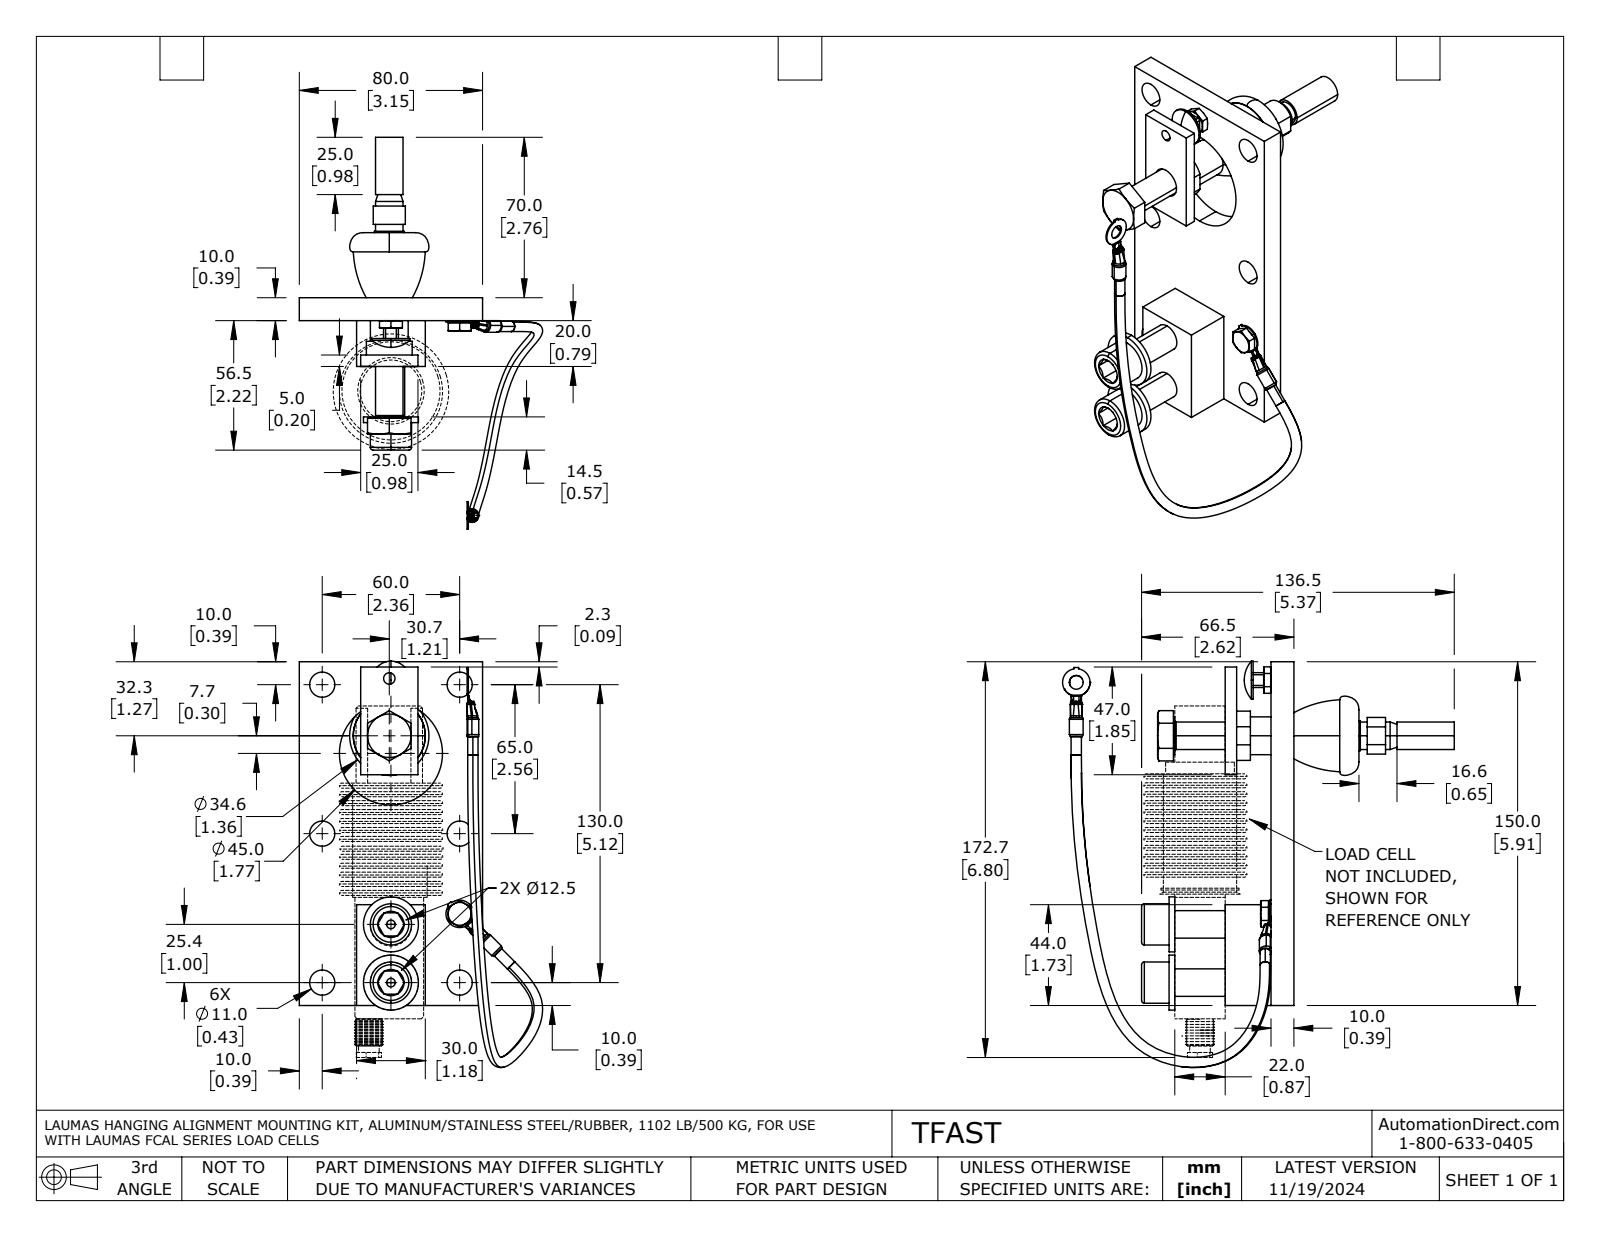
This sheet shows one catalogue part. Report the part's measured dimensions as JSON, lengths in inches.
{"part_name": "TFAST", "step_written_by": "SolidWorks 2021 (AUTOMOTIVE_DESIGN)", "units": "inches", "bodies": {"solids": 21, "faces": 555, "planar": 176, "cylindrical": 189, "other": 190}, "overall_size": [6.983, 6.732, 4.182], "volume_in3": 10.93, "surface_area_in2": 104, "round_holes": [[0.433, 6], [0.197, 3], [0.402, 3], [0.512, 3], [0.157, 2], [0.236, 2], [0.472, 2], [0.194, 1], [1.772, 1]], "round_bosses_or_shafts": [[0.472, 3], [0.945, 2], [0.709, 2], [0.177, 2], [0.655, 1], [0.652, 1], [0.65, 1], [0.512, 1]], "partial_cylinders_radius": [[0.021, 8], [0.043, 8], [0.052, 8], [0.035, 4], [0.039, 2], [0.118, 2], [0.119, 2], [0.138, 2]], "face_to_face_distances": [0.394, 0.984, 1.181, 0.787, 2.165, 0.866, 2.047, 3.15, 0.197, 0.591], "hole_center_spacings": [2.559, 3.483, 1.181, 1.67, 2.362, 0.304, 0.957, 0.984]}
